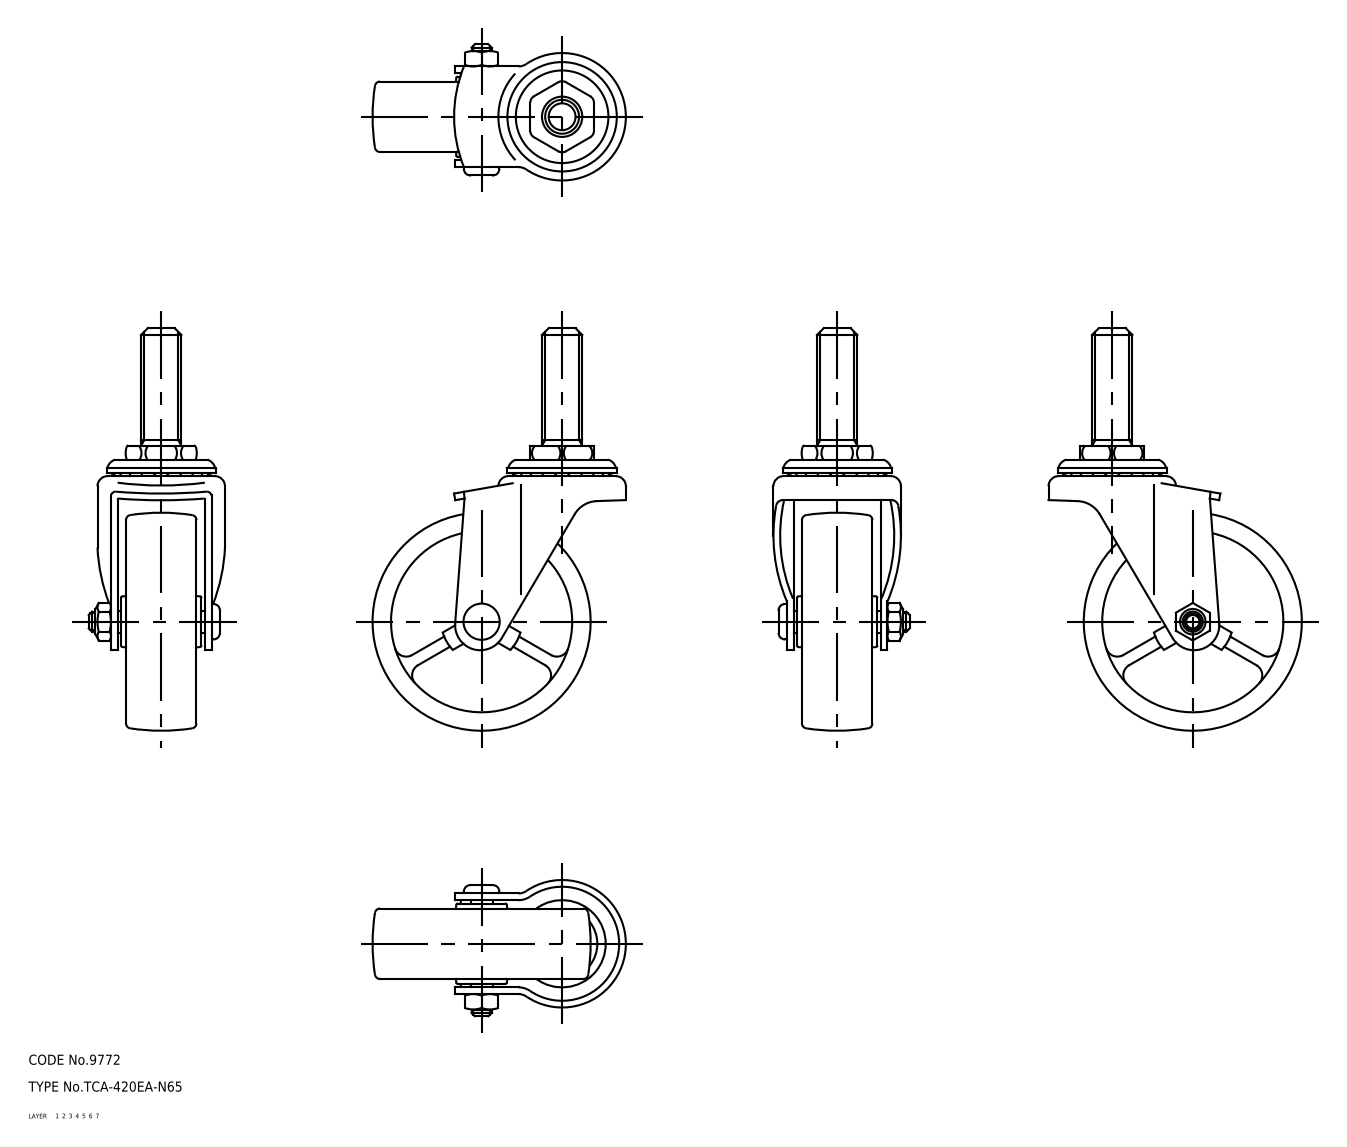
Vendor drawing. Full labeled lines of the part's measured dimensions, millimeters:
Part name (STEP PRODUCT): 67144007; 67144020; 67144033; 67144046 (+1 more)
STEP written by: CADfix (AUTOMOTIVE_DESIGN)
Units: millimetres
Bodies: 5 solids, 403 faces (0 planar, 0 cylindrical, 403 other)
Overall size (bounding box): 120 × 75.5 × 40.6
Volume: 68 888 mm³ · Surface area: 29 231 mm²
